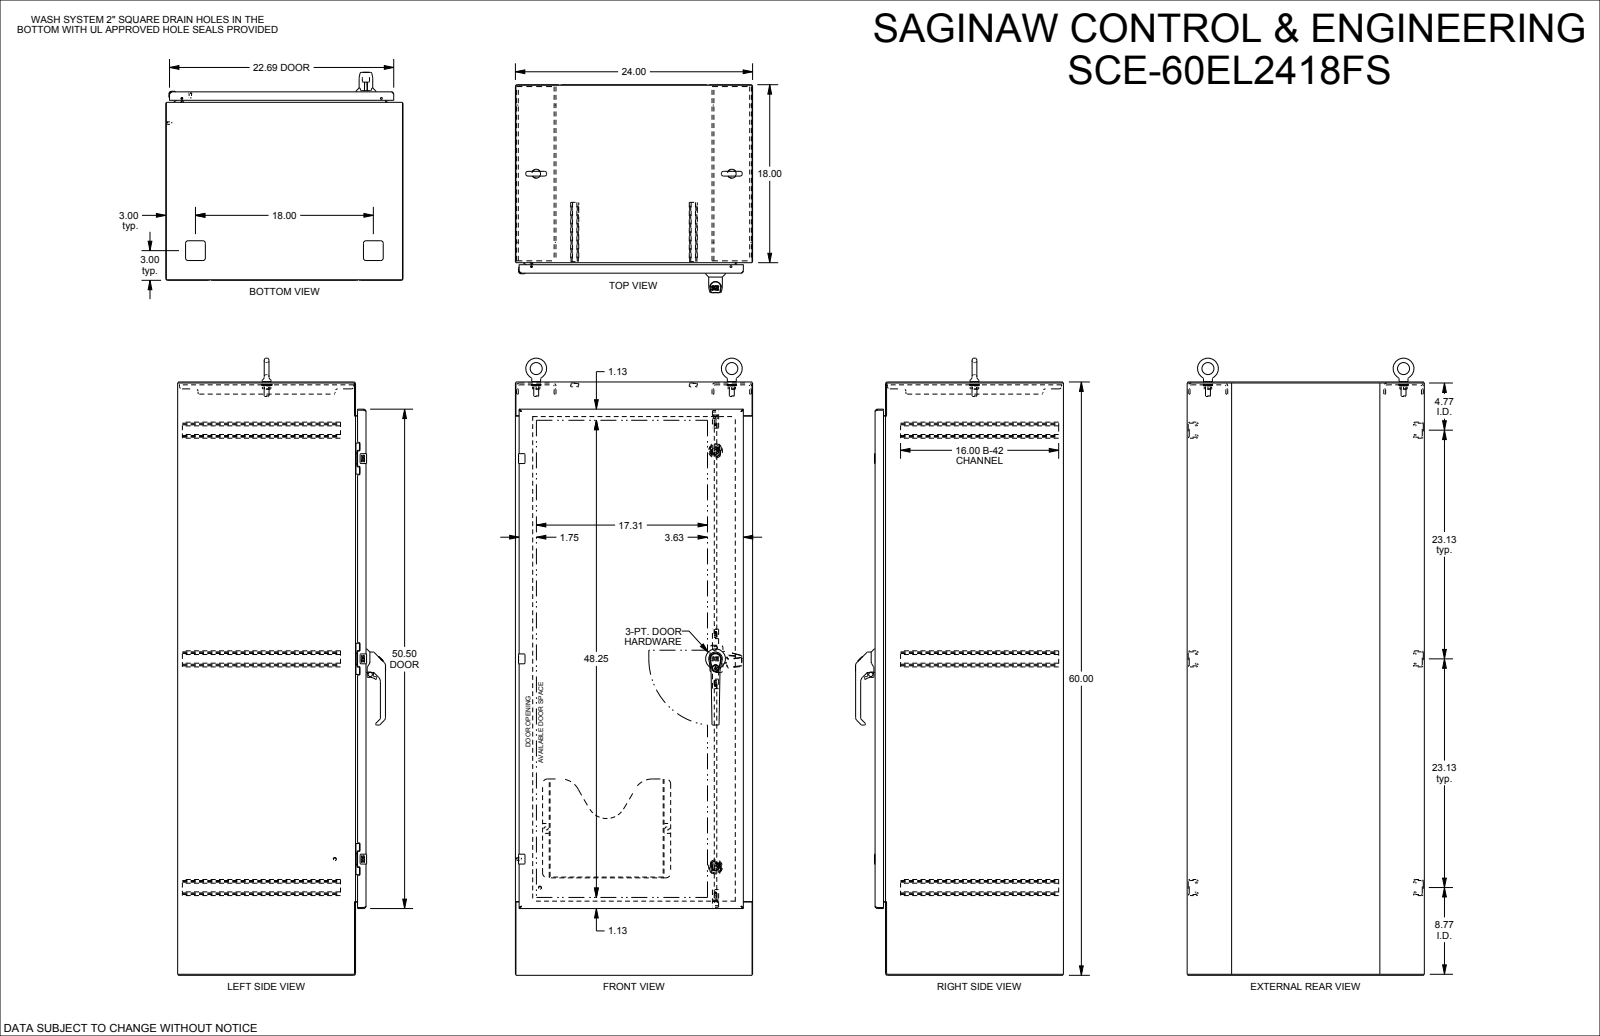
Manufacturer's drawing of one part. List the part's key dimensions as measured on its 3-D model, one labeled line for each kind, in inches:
Part name (STEP PRODUCT): SCE-60EL2418FS_REV5
STEP written by: SolidWorks 2021 (AUTOMOTIVE_DESIGN)
Units: inches
Bodies: 50 solids, 3976 faces (1613 planar, 1423 cylindrical, 940 other)
Overall size (bounding box): 62.289 × 24 × 21.038
Volume: 556.5 in³ · Surface area: 14 143 in²
Round holes (diameter × count): ⌀0.25 ×17, ⌀0.36 ×8, ⌀0.17 ×4, ⌀0.04 ×3, ⌀0.156 ×3, ⌀0.218 ×3, ⌀0.138 ×2, ⌀0.177 ×2, ⌀0.188 ×2, ⌀0.323 ×2, ⌀0.343 ×2, ⌀0.394 ×2
Round bosses / shafts (diameter × count): ⌀0.337 ×6, ⌀0.248 ×6, ⌀0.248 ×6, ⌀0.196 ×4, ⌀0.169 ×3, ⌀1.4 ×2, ⌀1.012 ×2, ⌀1 ×2
Partial cylindrical surfaces — rounded edges, fillets, slot ends (radius × count): R0.03 ×104, R0.015 ×62, R0.09 ×43, R0.18 ×36, R0.04 ×33, R0.02 ×32, R0.039 ×30, R0.125 ×28
Main face-to-face distances: 0.075, 23.925, 0.06, 19.058, 18.983, 18.998, 18.923, 23.85, 24, 59.925
Hole centre spacings: 20.25, 40.5, 0.592, 1.399, 1.4, 1.979, 1.979, 2.799
